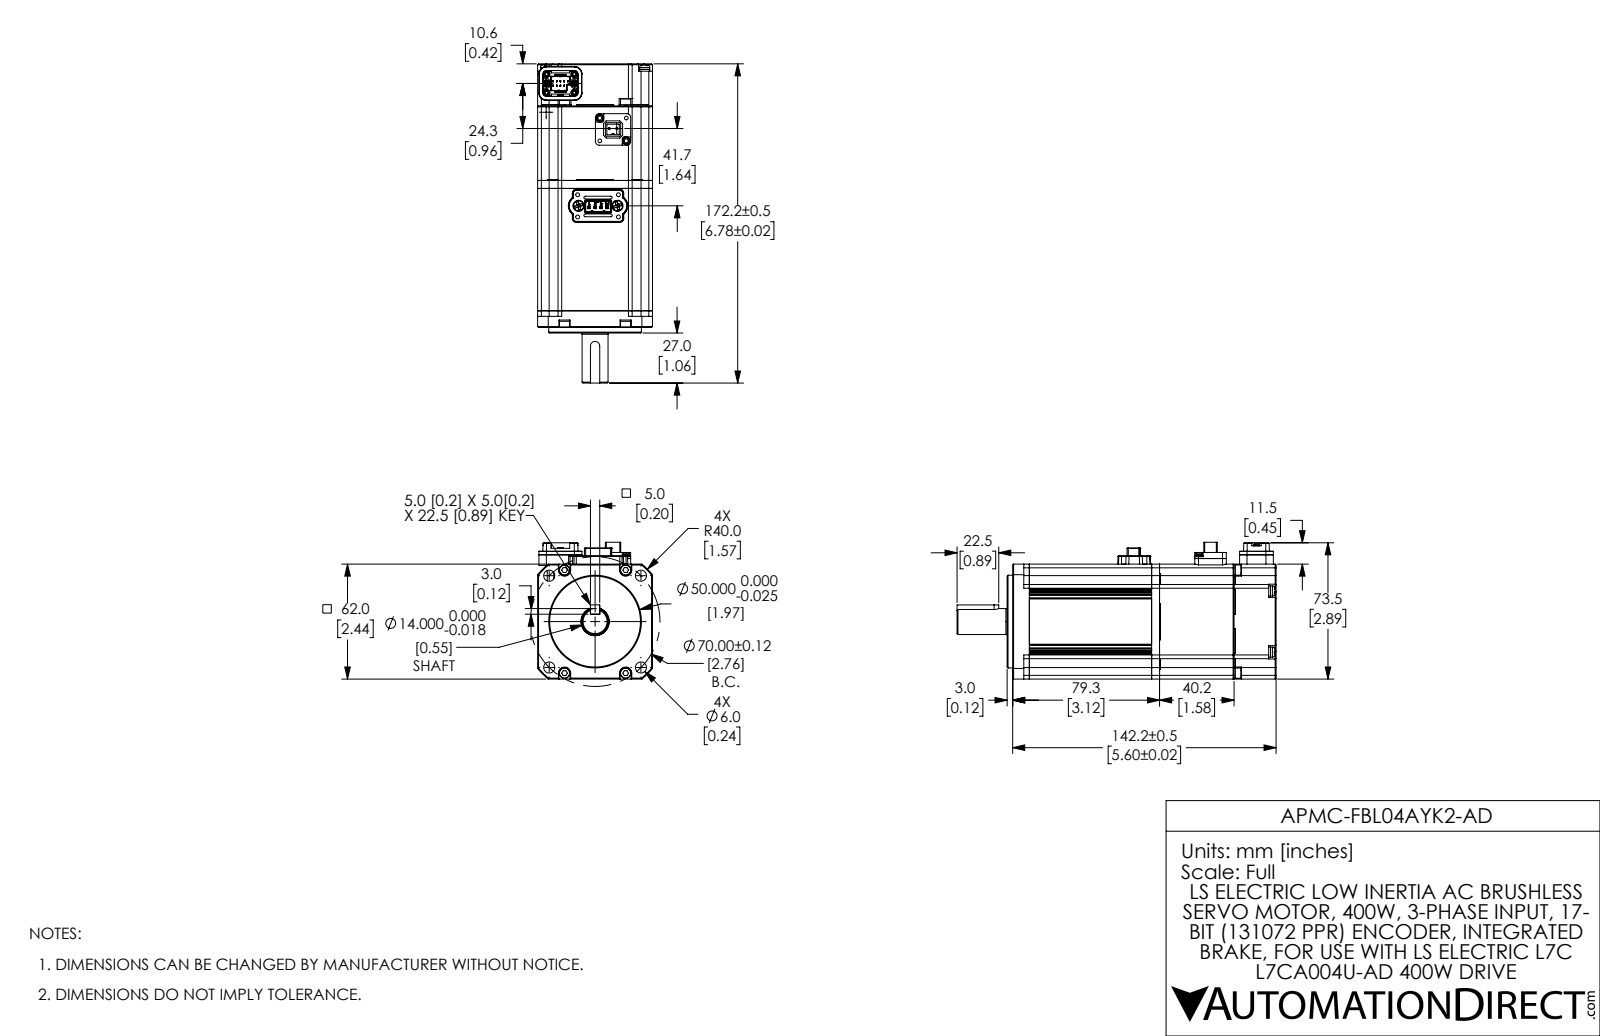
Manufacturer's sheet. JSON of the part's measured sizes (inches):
{"part_name": "APMC-FBL04AYK2-AD", "step_written_by": "SolidWorks 2017 (AUTOMOTIVE_DESIGN)", "units": "inches", "bodies": {"solids": 51, "faces": 2105, "planar": 1314, "cylindrical": 590, "other": 201}, "overall_size": [6.78, 2.906, 2.441], "volume_in3": 30.21, "surface_area_in2": 160, "round_holes": [[0.083, 10], [0.118, 10], [0.138, 8], [0.063, 6], [0.236, 6], [0.079, 4], [0.122, 4], [0.039, 2], [0.13, 1], [0.134, 1], [0.512, 1], [0.602, 1]], "round_bosses_or_shafts": [[0.213, 6], [0.22, 4], [0.217, 4], [0.165, 2], [0.142, 2], [0.138, 2], [0.087, 2], [0.035, 2]], "partial_cylinders_radius": [[0.008, 20], [0.012, 20], [0.039, 12], [0.079, 12], [0.118, 12], [0.006, 9], [0.018, 7], [0.004, 6]], "face_to_face_distances": [2.441, 0.028, 0.169, 0.02, 2.598, 2.768, 1.752, 1.583, 4.35, 1.61], "hole_center_spacings": [0.197, 0.237, 0.335, 0.346, 0.371, 0.602, 0.63, 0.879]}
